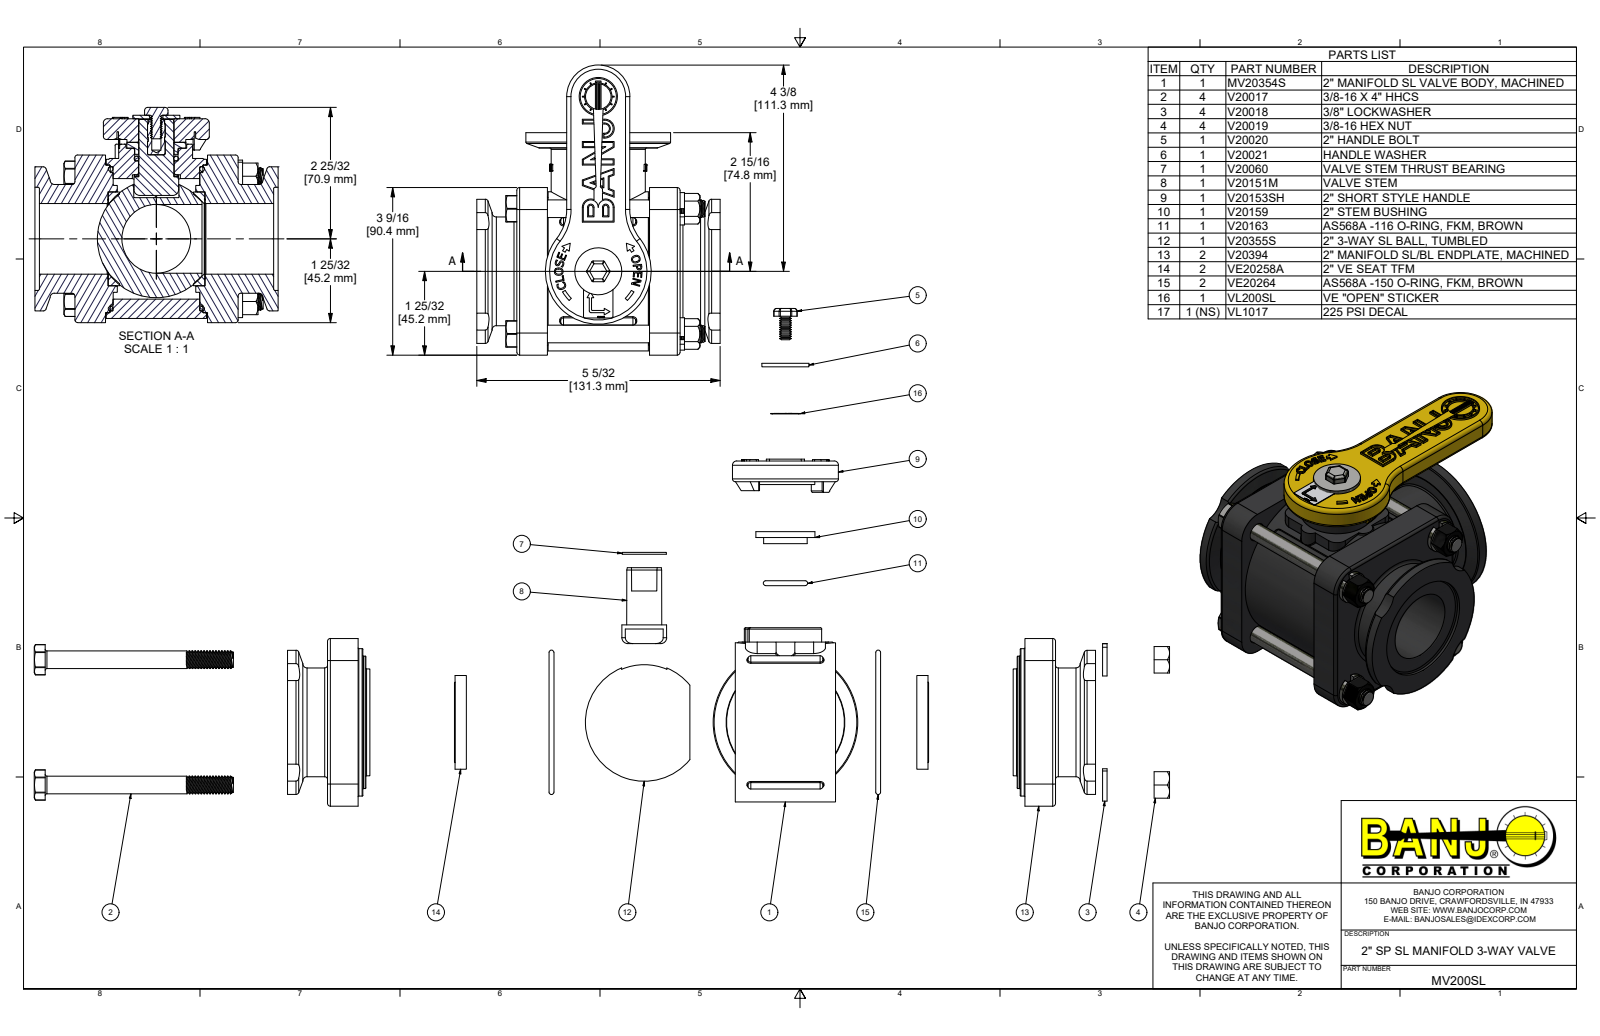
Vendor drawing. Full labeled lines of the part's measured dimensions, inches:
Part name (STEP PRODUCT): MV200SL; MV20354S; MV20354SX; V20151M (+8 more)
STEP written by: Autodesk Inventor 2022 (AUTOMOTIVE_DESIGN)
Units: inches
Bodies: 29 solids, 2159 faces (923 planar, 476 cylindrical, 760 other)
Overall size (bounding box): 6.16 × 5.169 × 4.571
Volume: 41.19 in³ · Surface area: 301.5 in²
Round holes (diameter × count): ⌀0.307 ×4, ⌀0.385 ×4, ⌀0.406 ×4, ⌀1.46 ×2, ⌀0.196 ×1, ⌀0.281 ×1, ⌀0.351 ×1, ⌀0.375 ×1, ⌀0.544 ×1, ⌀0.75 ×1, ⌀0.751 ×1, ⌀0.76 ×1
Round bosses / shafts (diameter × count): ⌀0.324 ×60, ⌀0.687 ×4, ⌀0.375 ×4, ⌀3.38 ×1, ⌀3.13 ×1, ⌀3.074 ×1, ⌀2.812 ×1, ⌀2.31 ×1
Partial cylindrical surfaces — rounded edges, fillets, slot ends (radius × count): R0.06 ×18, R0.03 ×17, R0.09 ×10, R0.02 ×8, R0.125 ×8, R0.162 ×8, R0.031 ×4, R0.21 ×4
Main face-to-face distances: 0.65, 2.819, 0.85, 3.669, 3.469, 1.5, 4.319, 3.56, 0.1, 0.05
Hole centre spacings: 1.88, 2.659, 3.761, 3.71
